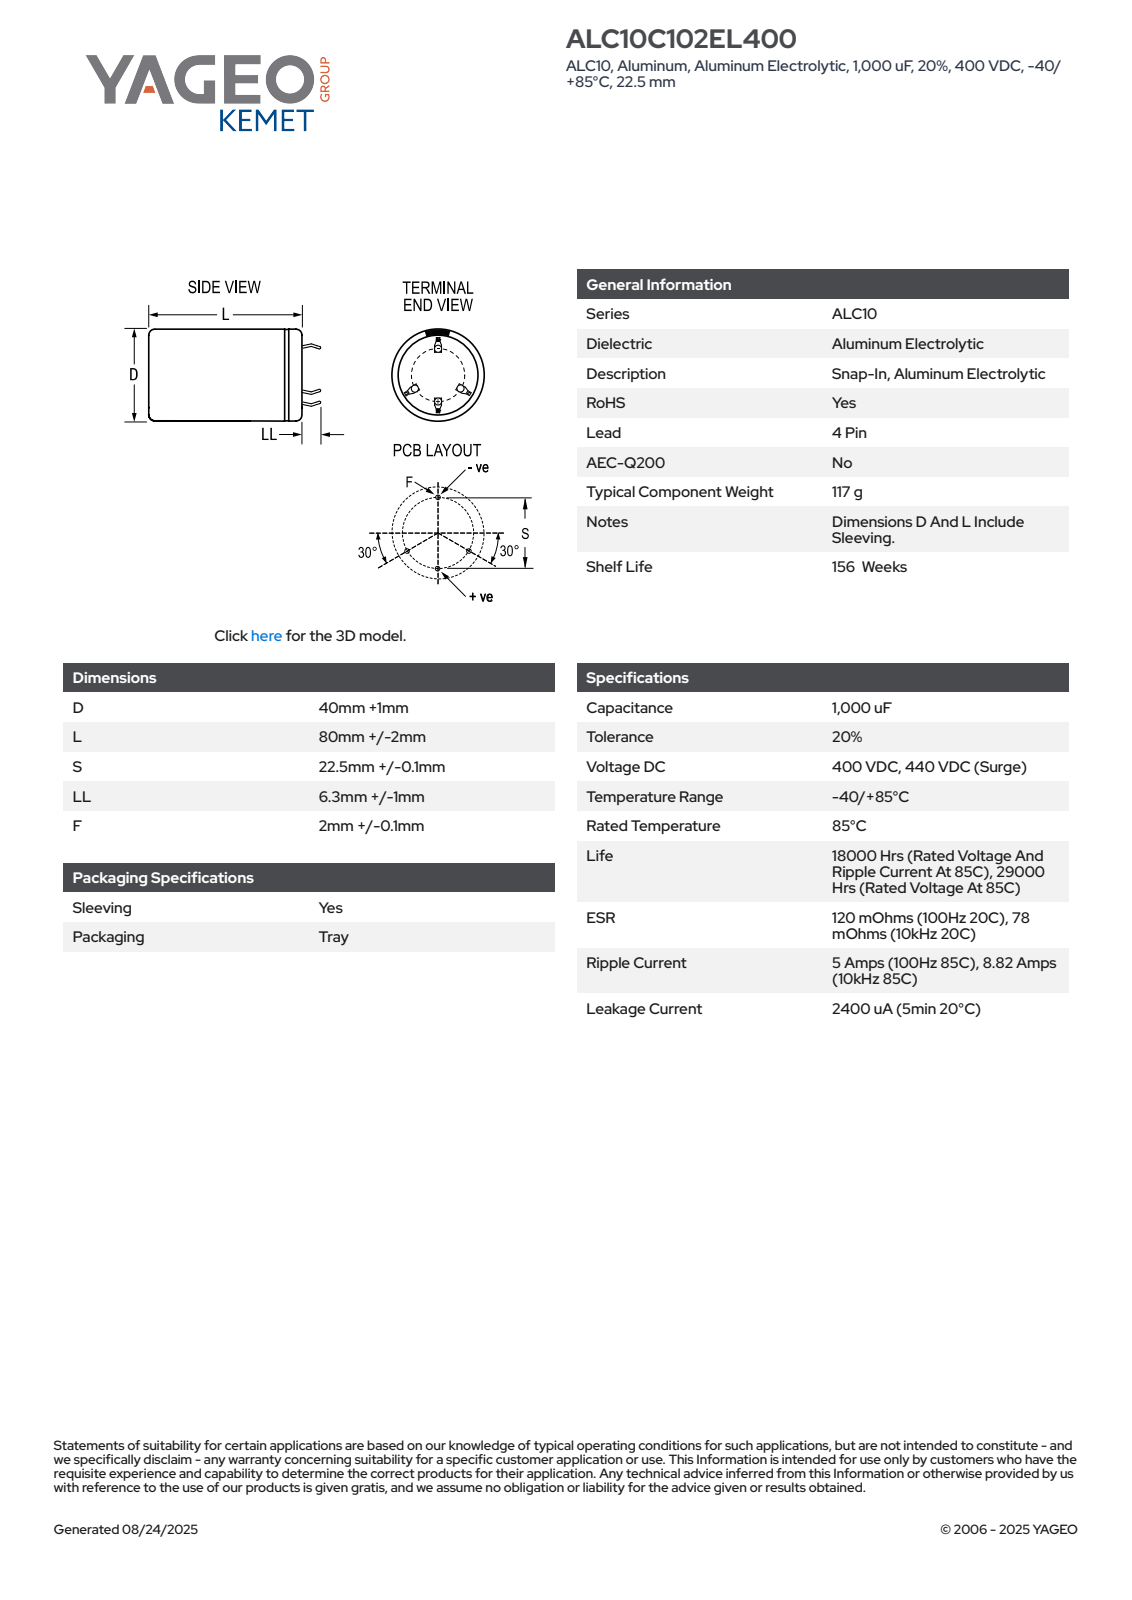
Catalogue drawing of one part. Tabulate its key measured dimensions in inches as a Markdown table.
| quantity | value |
| --- | --- |
| part name | CARS_K4P_40X80_D41L82S22.5LL7.3F2.1 |
| STEP written by | SolidWorks 2014 (AUTOMOTIVE_DESIGN) |
| units | inches |
| bodies | 1 solid, 134 faces (80 planar, 15 cylindrical, 39 other) |
| overall size | 3.515 × 1.614 × 1.614 |
| volume | 6.559 in³ |
| surface area | 20.54 in² |
| round holes (diameter × count) | 1.428 × 1 |
| round bosses / shafts (diameter × count) | 1.614 × 1 |
| partial cylindrical surfaces (radius × count) | 0.807 × 1 |
| main face-to-face distances | 3.228, 3.248, 0.02, 0.024, 0.014, 0.738, 0.014, 0.03, 0.053, 0.724 |
